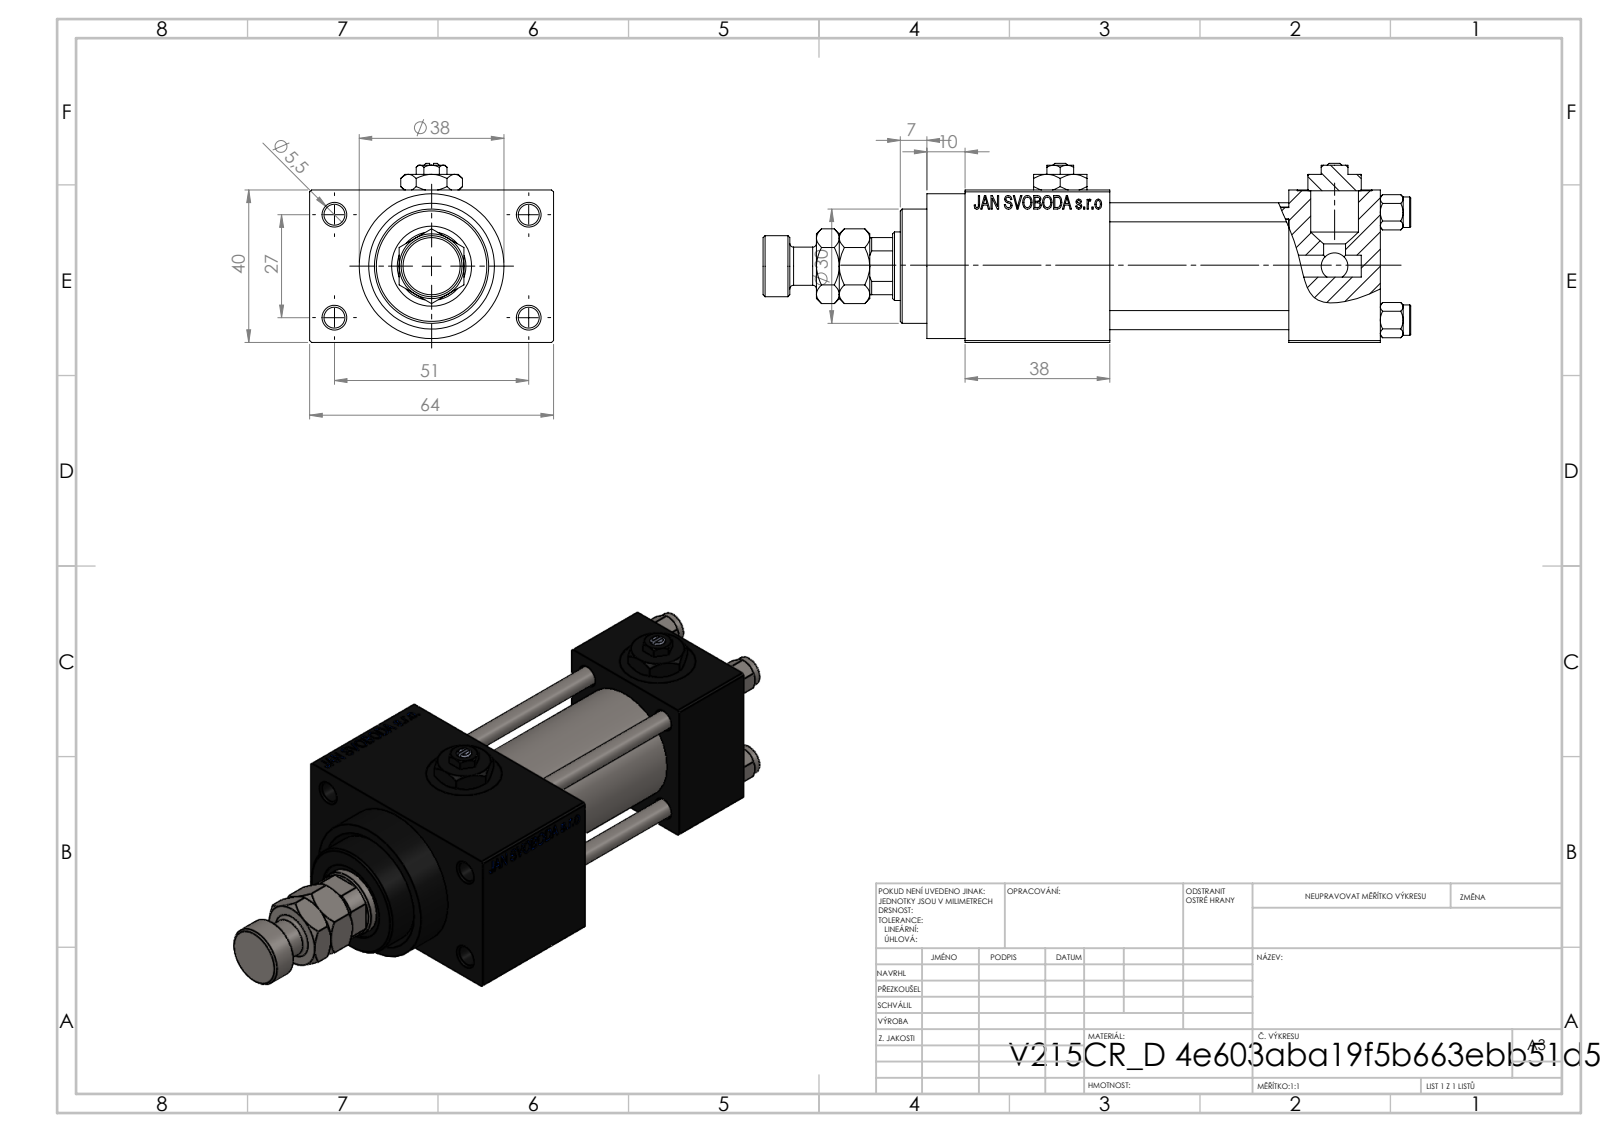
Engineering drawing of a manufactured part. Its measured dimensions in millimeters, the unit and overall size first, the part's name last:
Units: millimetres
Overall size (bounding box): 170 × 64 × 47
Round holes (diameter × count): ⌀20 ×5, ⌀5 ×4, ⌀5.5 ×4, ⌀13.16 ×4, ⌀7 ×3, ⌀8.5 ×1, ⌀18 ×1, ⌀21 ×1, ⌀25 ×1, ⌀30 ×1
Round bosses / shafts (diameter × count): ⌀8 ×4, ⌀38 ×1, ⌀31 ×1, ⌀16 ×1, ⌀10 ×1
Partial cylindrical surfaces — rounded edges, fillets, slot ends (radius × count): R8.5 ×1
Main face-to-face distances: 40, 12, 47, 71, 52, 24, 38, 85, 109, 64
Hole centre spacings: 11.37, 20.01, 28.3, 28.85, 29.89, 39.66, 48.34, 27
Volume: 183 524 mm³ · Surface area: 68 340 mm²
Bodies: 14 solids, 1252 faces (557 planar, 101 cylindrical, 594 other)
Part name (STEP PRODUCT): V215CR_D_TYCINKA; Zatka_pro_OIL_PORT; MFA; V215CR_VCP_D (+3 more)
STEP written by: SolidWorks 2019 (CONFIG_CONTROL_DESIGN)
